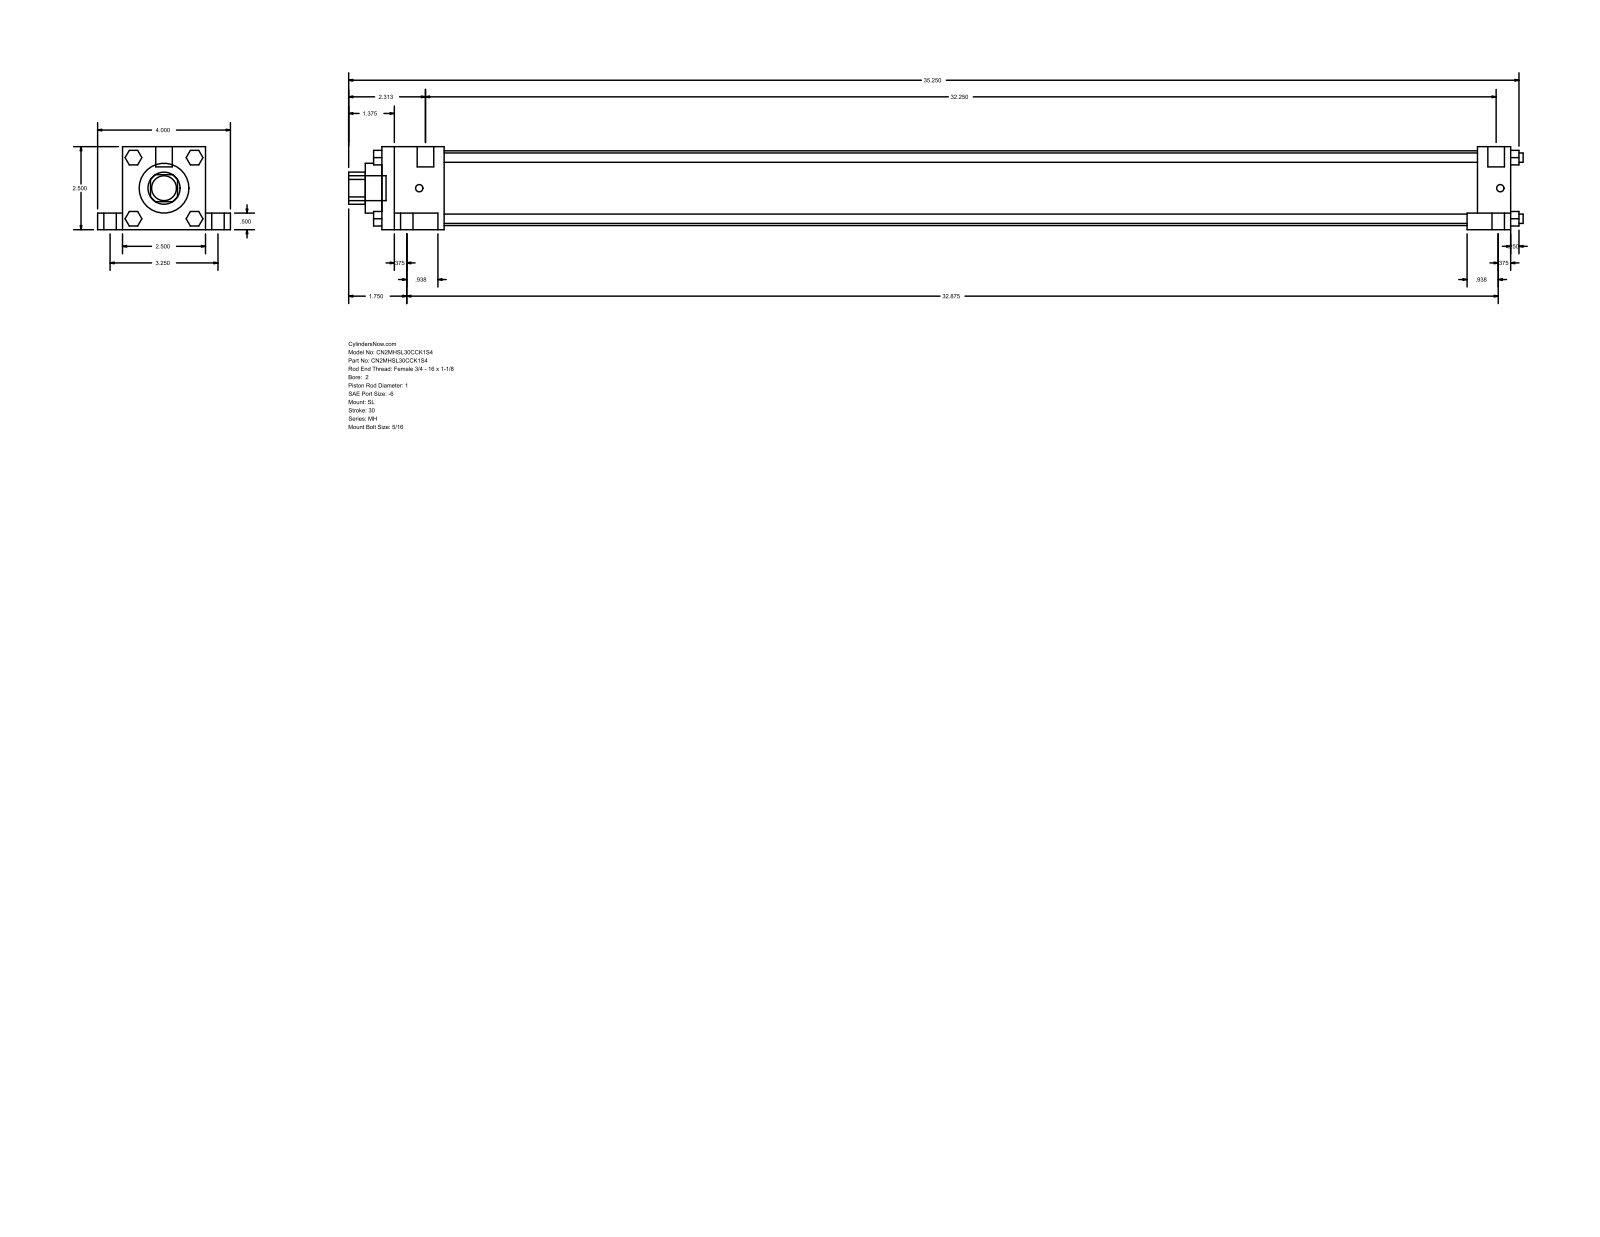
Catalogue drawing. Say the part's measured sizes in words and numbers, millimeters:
The part is named "MH_SL__0200_1". Its 3-D file was written by "GSSL Pune (CONFIG_CONTROL_DESIGN)". It is 0 solids with 148 faces: 112 planar, 36 cylindrical and 0 other. Overall it measures 898.52 by 101.6 by 63.5 millimeters. Round holes: 1 of diameter 25.4, 1 of diameter 38.1, 1 of diameter 57.15. Round bosses or shafts: 4 of diameter 15.88, 4 of diameter 9.53, 4 of diameter 7.14, 4 of diameter 5.56, 2 of diameter 12.7, 1 of diameter 19.05. Partial cylindrical surfaces (rounded edges, fillets, slot ends): 1 of radius 12.29. The main face-to-face distances are 63.5, 863.6, 12.7, 19.05, 50.8, 82.55, 9.52, 25.4, 838.2, 47.63.
